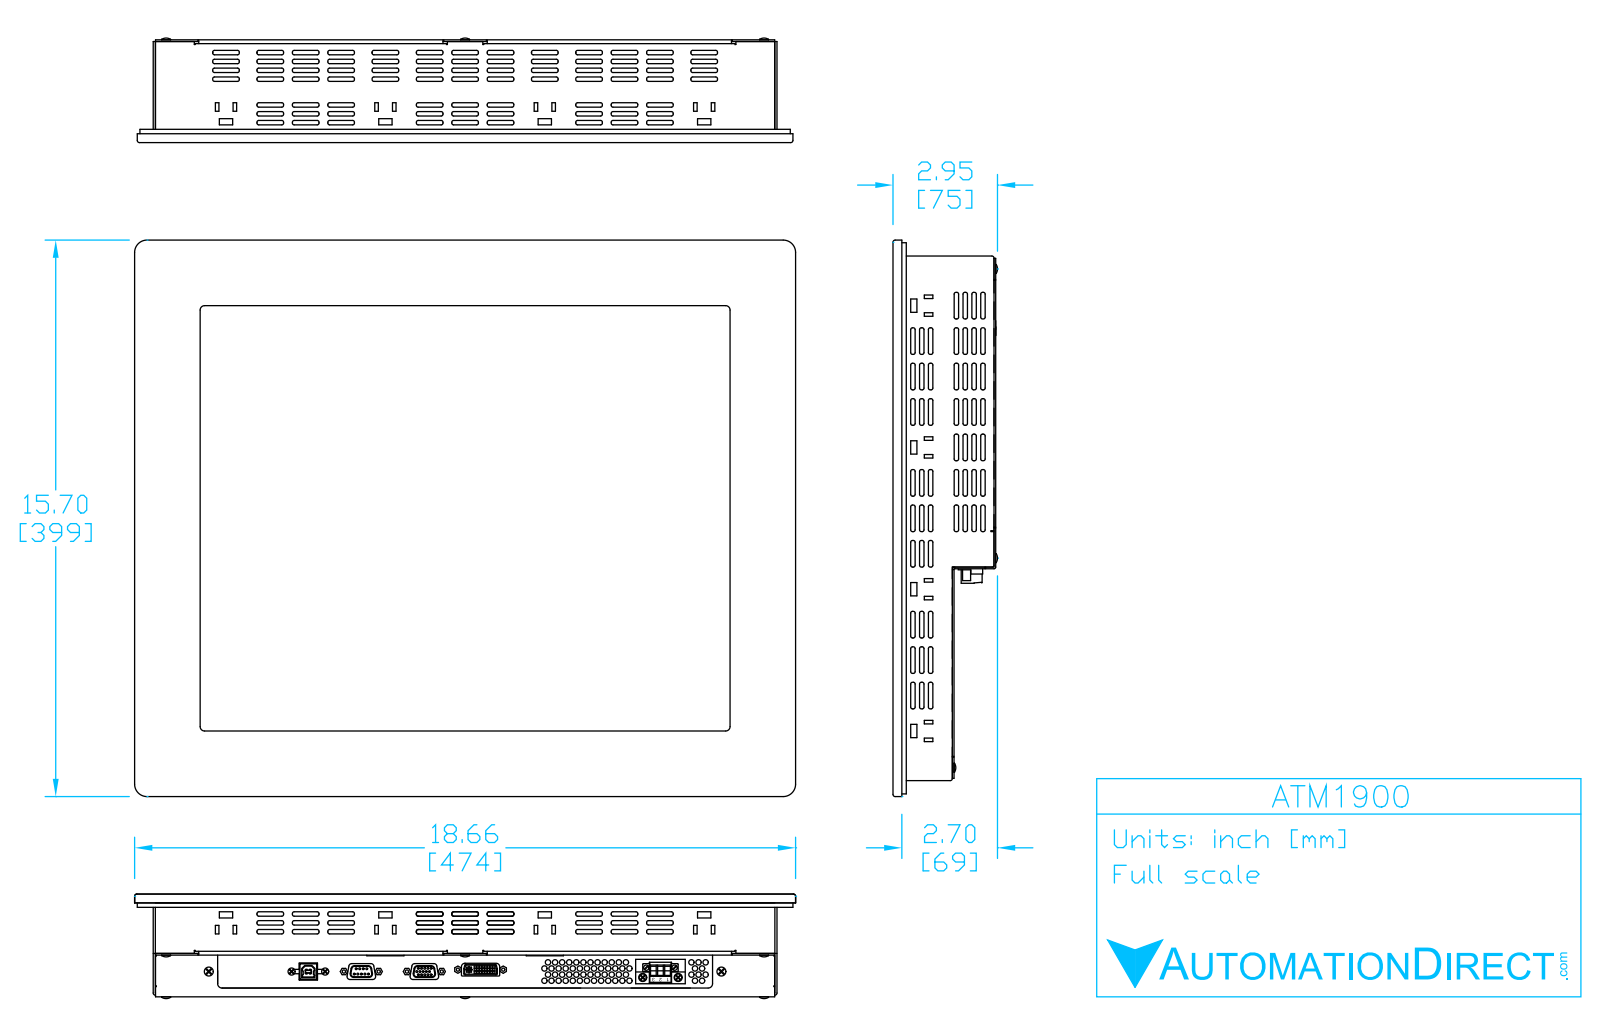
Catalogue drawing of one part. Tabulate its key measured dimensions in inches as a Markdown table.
| quantity | value |
| --- | --- |
| part name | ATM1900 |
| STEP written by | SolidWorks 2017 (AUTOMOTIVE_DESIGN) |
| units | inches |
| bodies | 59 solids, 2363 faces (1761 planar, 518 cylindrical, 84 other) |
| overall size | 18.661 × 15.718 × 2.9 |
| volume | 81.49 in³ |
| surface area | 1 543 in² |
| round holes (diameter × count) | 0.15 × 62, 0.156 × 16, 0.05 × 15, 0.087 × 2, 0.09 × 2, 0.225 × 2, 0.36 × 1 |
| round bosses / shafts (diameter × count) | 0.362 × 16, 0.24 × 16, 0.186 × 16, 0.2 × 6, 0.125 × 4, 0.22 × 2, 0.125 × 2 |
| partial cylindrical surfaces (radius × count) | 0.083 × 28, 0.01 × 20, 0.08 × 7, 0.015 × 6, 0.04 × 6, 0.06 × 6, 0.1 × 6, 0.05 × 4 |
| main face-to-face distances | 0.06, 0.06, 0.141, 2.59, 2.731, 2.65, 2.791, 2.9, 2.84, 0.25 |
| hole center spacings | 0.101, 0.162, 0.09, 0.18, 0.202, 0.18, 0.243, 0.27 |
